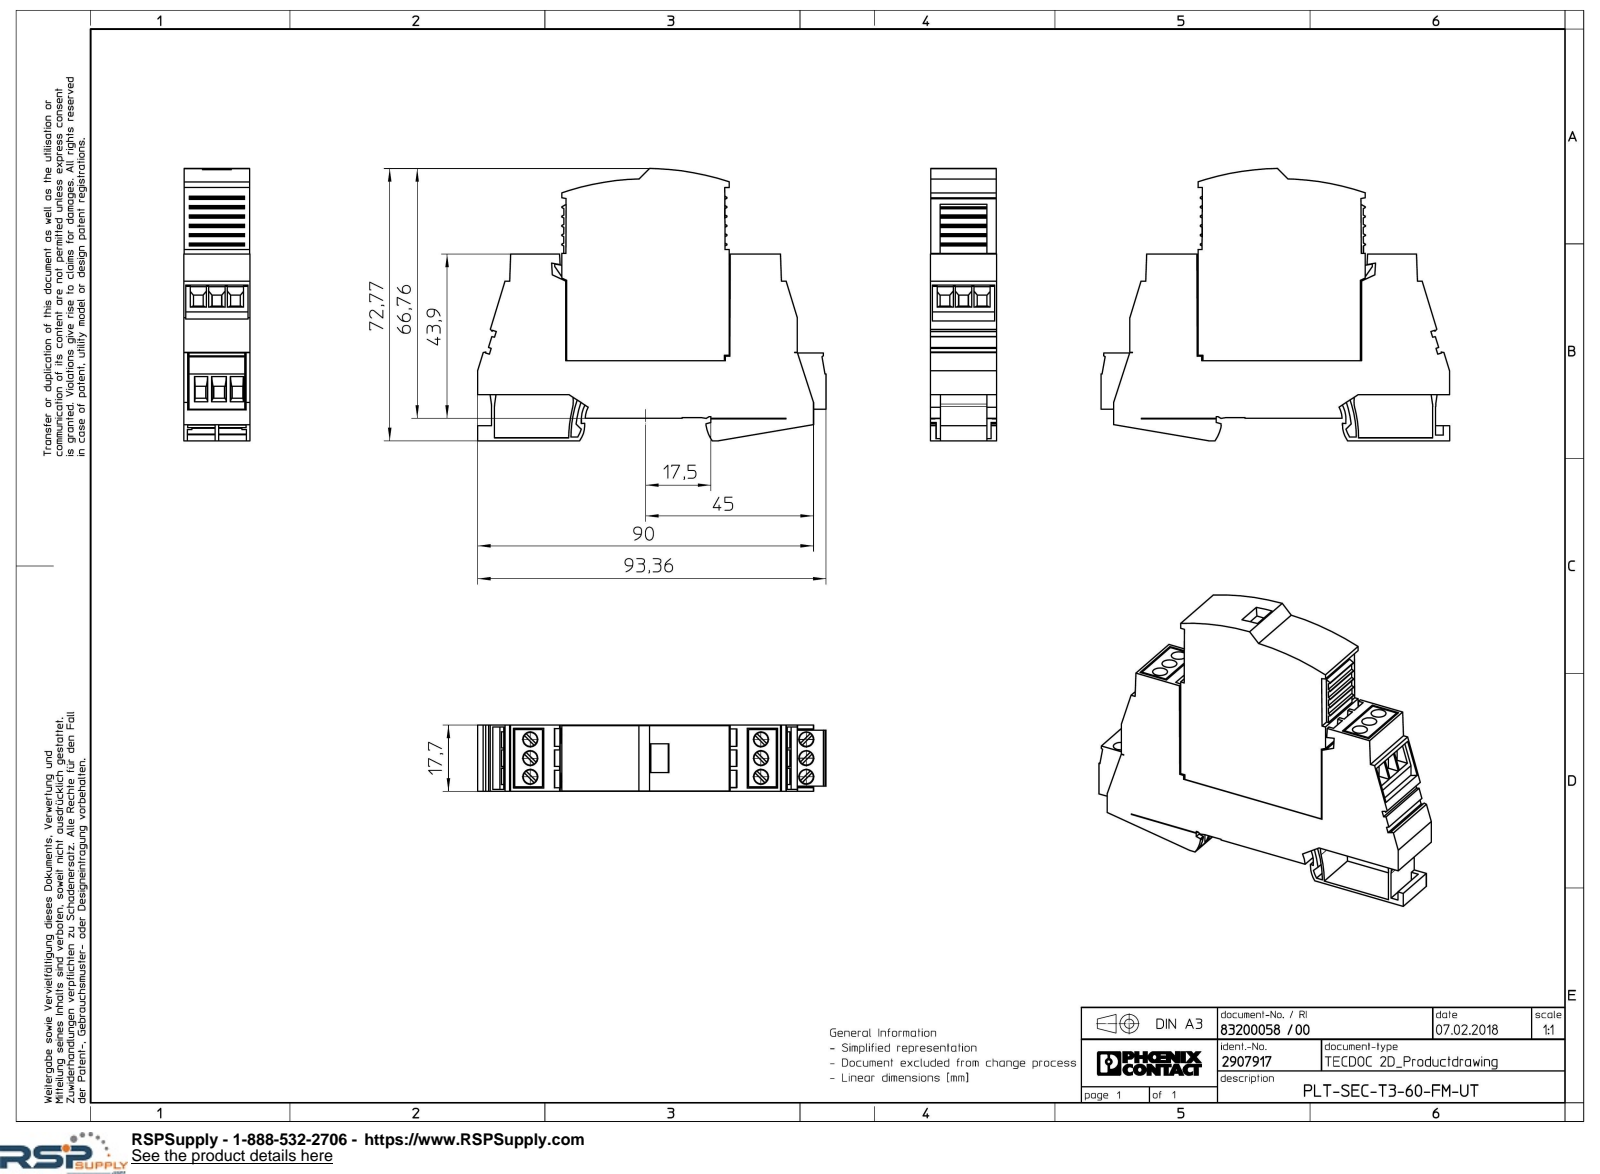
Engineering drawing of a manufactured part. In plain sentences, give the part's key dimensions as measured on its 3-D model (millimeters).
The part is named "PLT_SEC_T3...FM_UT-select". Its 3-D file was written by "Creo Elements/Direct Modeling 20.1A 29-Sep-2018 (C) Parametric Technology GmbH (AUTOMOTIVE_DESIGN)". It is 1 solid with 543 faces: 484 planar, 55 cylindrical and 4 other. Overall it measures 93.36 by 72.77 by 17.7 millimeters. Its volume is 75 573 cubic millimeters and its surface area 22 474 square millimeters. Round holes: 9 of diameter 4. Round bosses or shafts: 9 of diameter 3.8. Partial cylindrical surfaces (rounded edges, fillets, slot ends): 2 of radius 0.2, 1 of radius 0.5, 1 of radius 0.6, 1 of radius 1, 1 of radius 5, 1 of radius 7, 1 of radius 7.3, 1 of radius 7.72. The main face-to-face distances are 17.6, 17.7, 17.5, 6.29, 43.5, 6.01, 12.3, 0.36, 49.92, 43.91. The hole center spacings are 5, 13.14, 62.02, 74.14, 10, 12.15, 61.82, 73.97.
